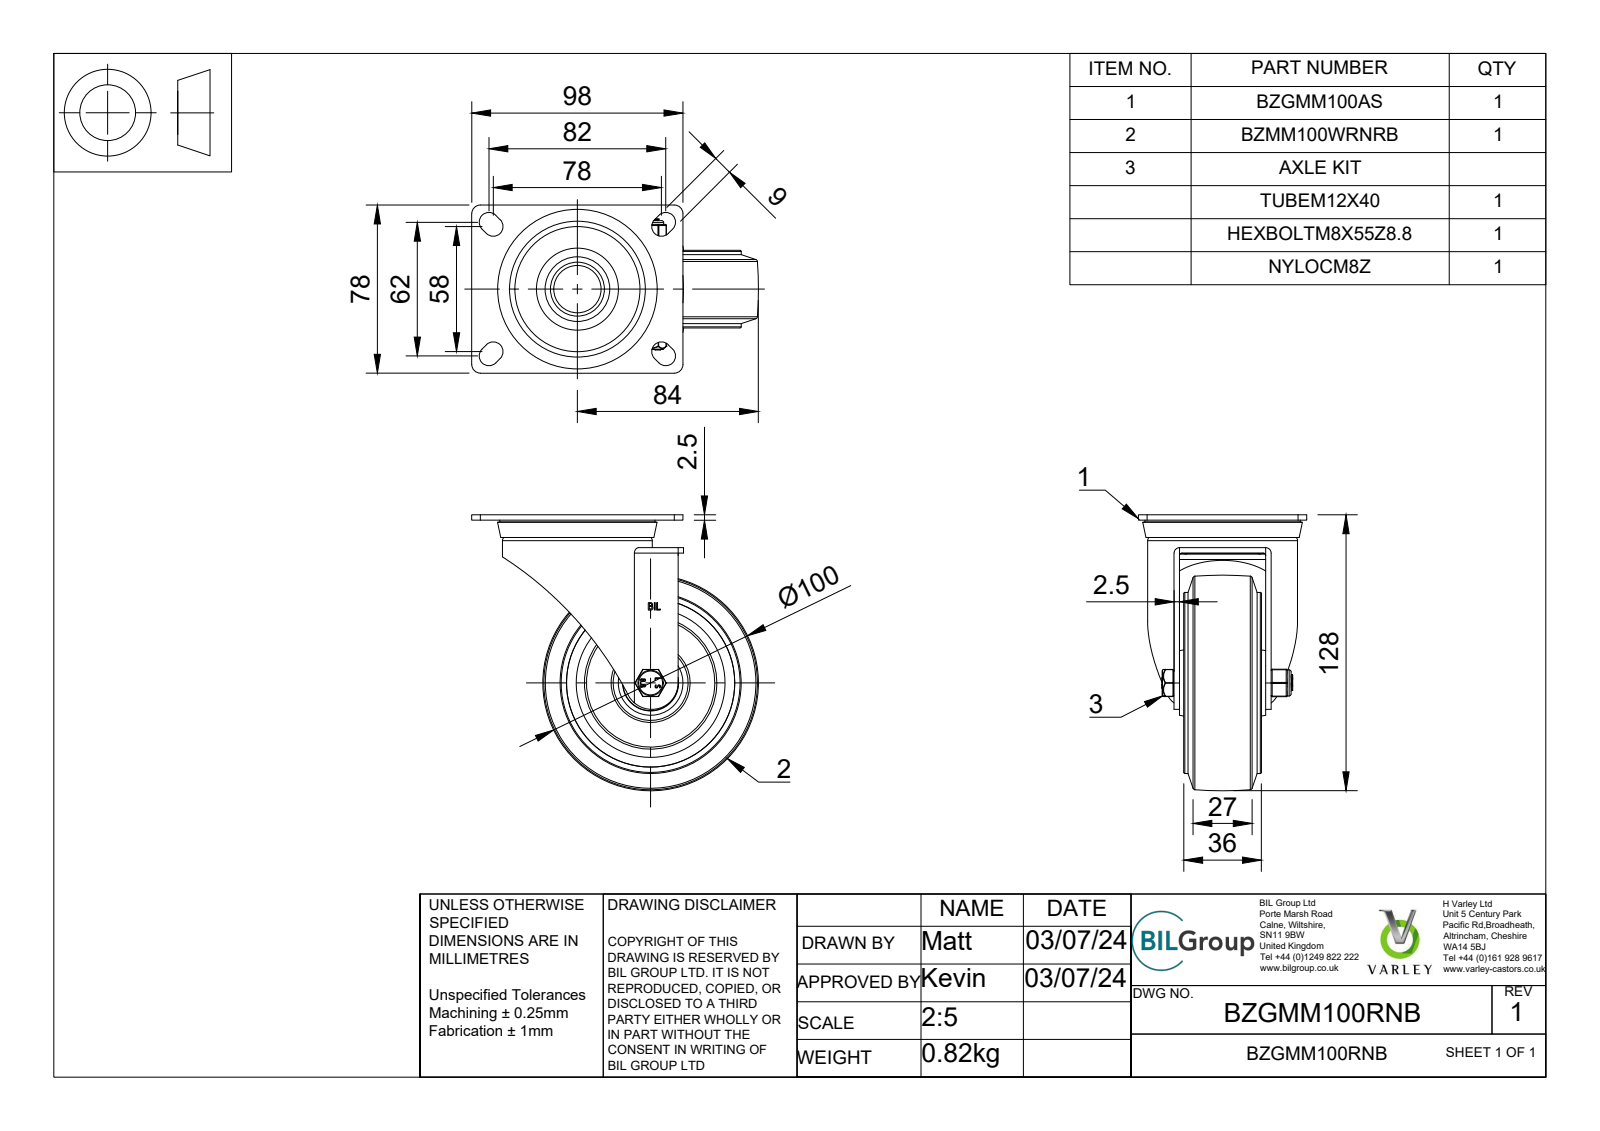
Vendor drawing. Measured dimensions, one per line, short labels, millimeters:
name: BZGMM100RNB v3; BZGMM100AS - 2 v1; ZINC PLATED, PRESSED STEEL TOP PLATE; ZINC PLATED, PRESSED STEEL TOP PLATE Geometry (+7 more)
written by: Autodesk Translation Framework v13.14.0.145 (AUTOMOTIVE_DESIGN)
unit: mm
bodies: 46 solids, 483 faces (191 planar, 163 cylindrical, 129 other)
size: 133 × 128 × 78
volume: 280 328 mm³; area: 119 308 mm²
holes: 2× ⌀0.66, 2× ⌀26, 1× ⌀8, 1× ⌀8.2, 1× ⌀8.4, 1× ⌀8.6, 1× ⌀12.5, 1× ⌀20, 1× ⌀30, 1× ⌀64.5, 1× ⌀78
bosses: 8× ⌀3.75, 1× ⌀84, 1× ⌀69.5, 1× ⌀47, 1× ⌀25, 1× ⌀19.5, 1× ⌀12.1, 1× ⌀11.9
rounds: 18× R0.5, 12× R0.25, 8× R4.5, 4× R0.33, 4× R0.64, 4× R1.25, 4× R4, 2× R0.63
face distances: 2.5, 2, 10, 4.5, 23, 15, 25, 38, 13, 27.5
hole spacings: 3.22, 2.49
